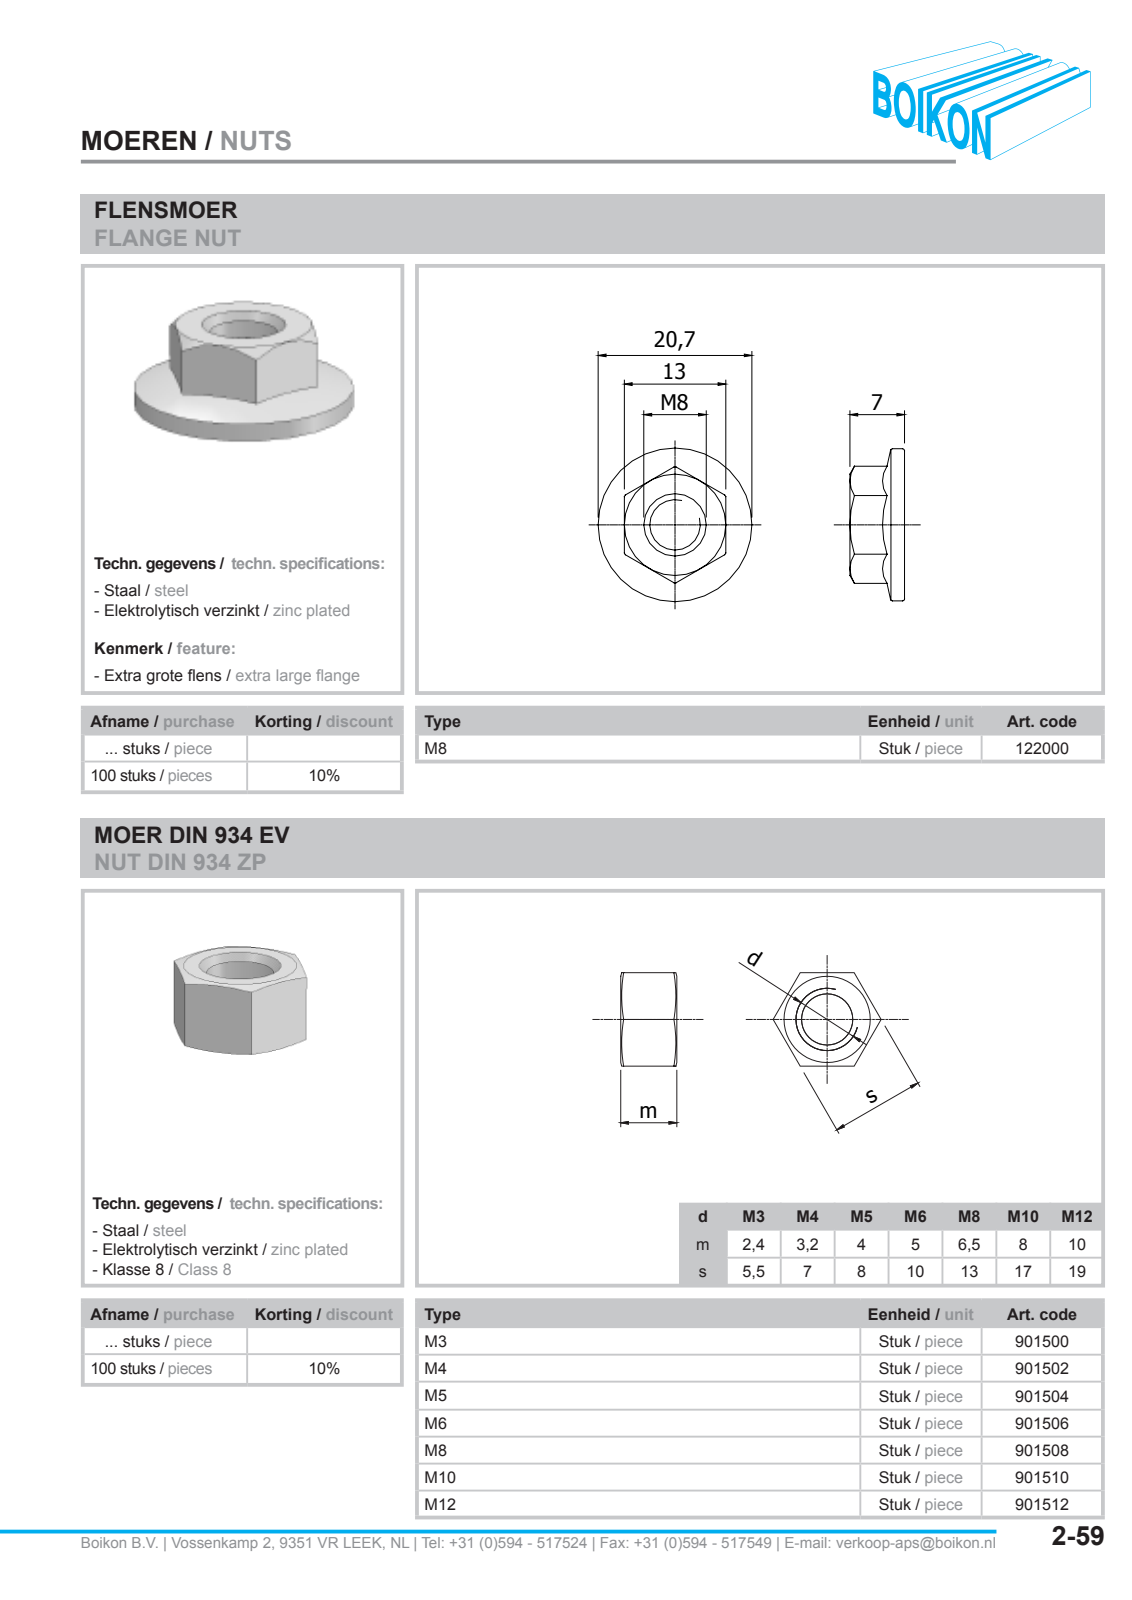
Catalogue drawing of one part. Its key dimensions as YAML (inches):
part_name: "Root; 122000Flensmoer M8BOIKON"
step_written_by: "HiCAD 2013 1802.4 Build 509 (AUTOMOTIVE_DESIGN)"
units: inches
bodies: {solids: 1, faces: 25, planar: 14, cylindrical: 2, other: 9}
overall_size: [0.827, 0.827, 0.315]
volume: 0.074
surface_area: 1.765
round_holes:
  - {diameter: 0.315, count: 1}
round_bosses_or_shafts:
  - {diameter: 0.827, count: 1}
face_to_face_distances: [0.512, 0.315, 0.276, 0.039]
